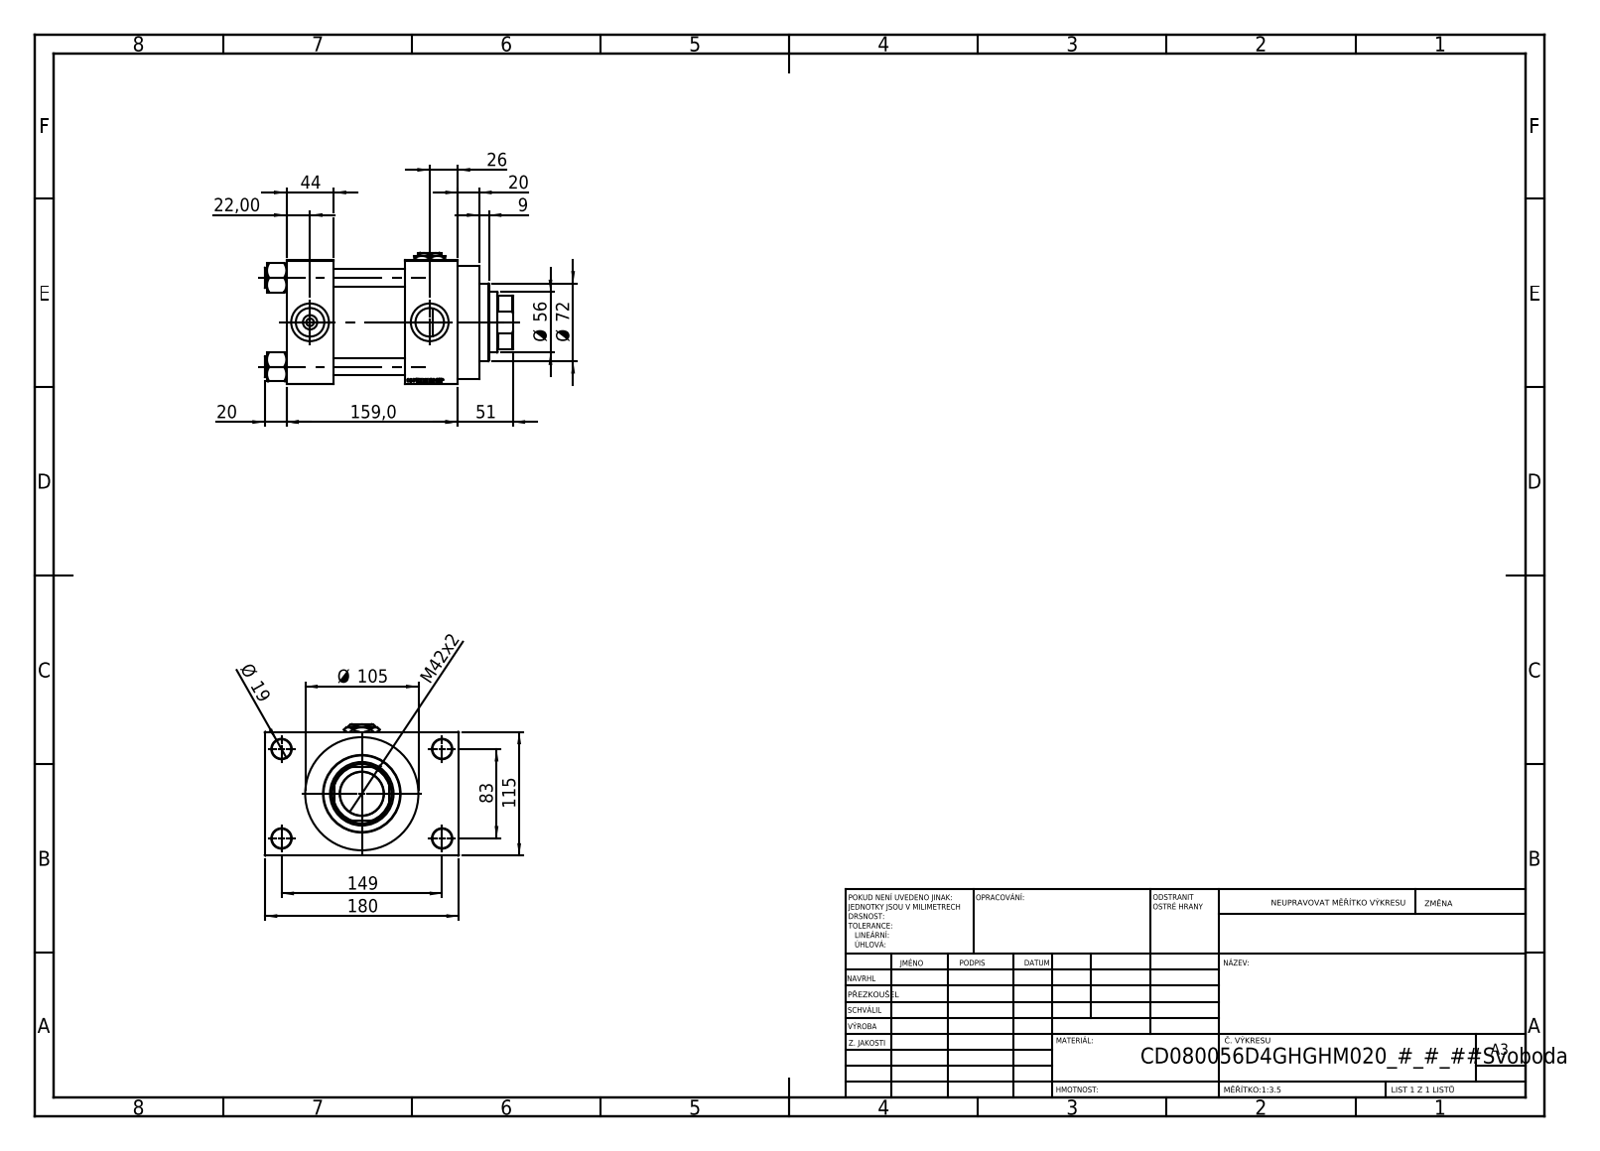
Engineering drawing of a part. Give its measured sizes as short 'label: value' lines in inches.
name: V215CD_NUT_M5_D; V215CD_VCP_D; V215CD_D_Body; V215CD_VC_A (+2 more)
written by: SolidWorks 2019 (CONFIG_CONTROL_DESIGN)
unit: in
bodies: 12 solids, 1196 faces (568 planar, 90 cylindrical, 538 other)
size: 9.055 × 7.087 × 4.803
volume: 127.6 in³; area: 486.2 in²
holes: 4× ⌀0.63, 4× ⌀0.709, 3× ⌀1.041, 3× ⌀1.378, 2× ⌀0.276, 1× ⌀1.594, 1× ⌀2.205, 1× ⌀2.323, 1× ⌀2.402, 1× ⌀2.835, 1× ⌀3.15
bosses: 4× ⌀0.748, 1× ⌀4.134, 1× ⌀3.386
rounds: 1× R1.063
face distances: 4.528, 2.598, 4.331, 1.732, 6.26, 1.929, 1.28, 5.807, 0.787, 2.717
hole spacings: 1.305, 2.302, 3.256, 3.357, 3.513, 4.561, 5.607, 3.268
